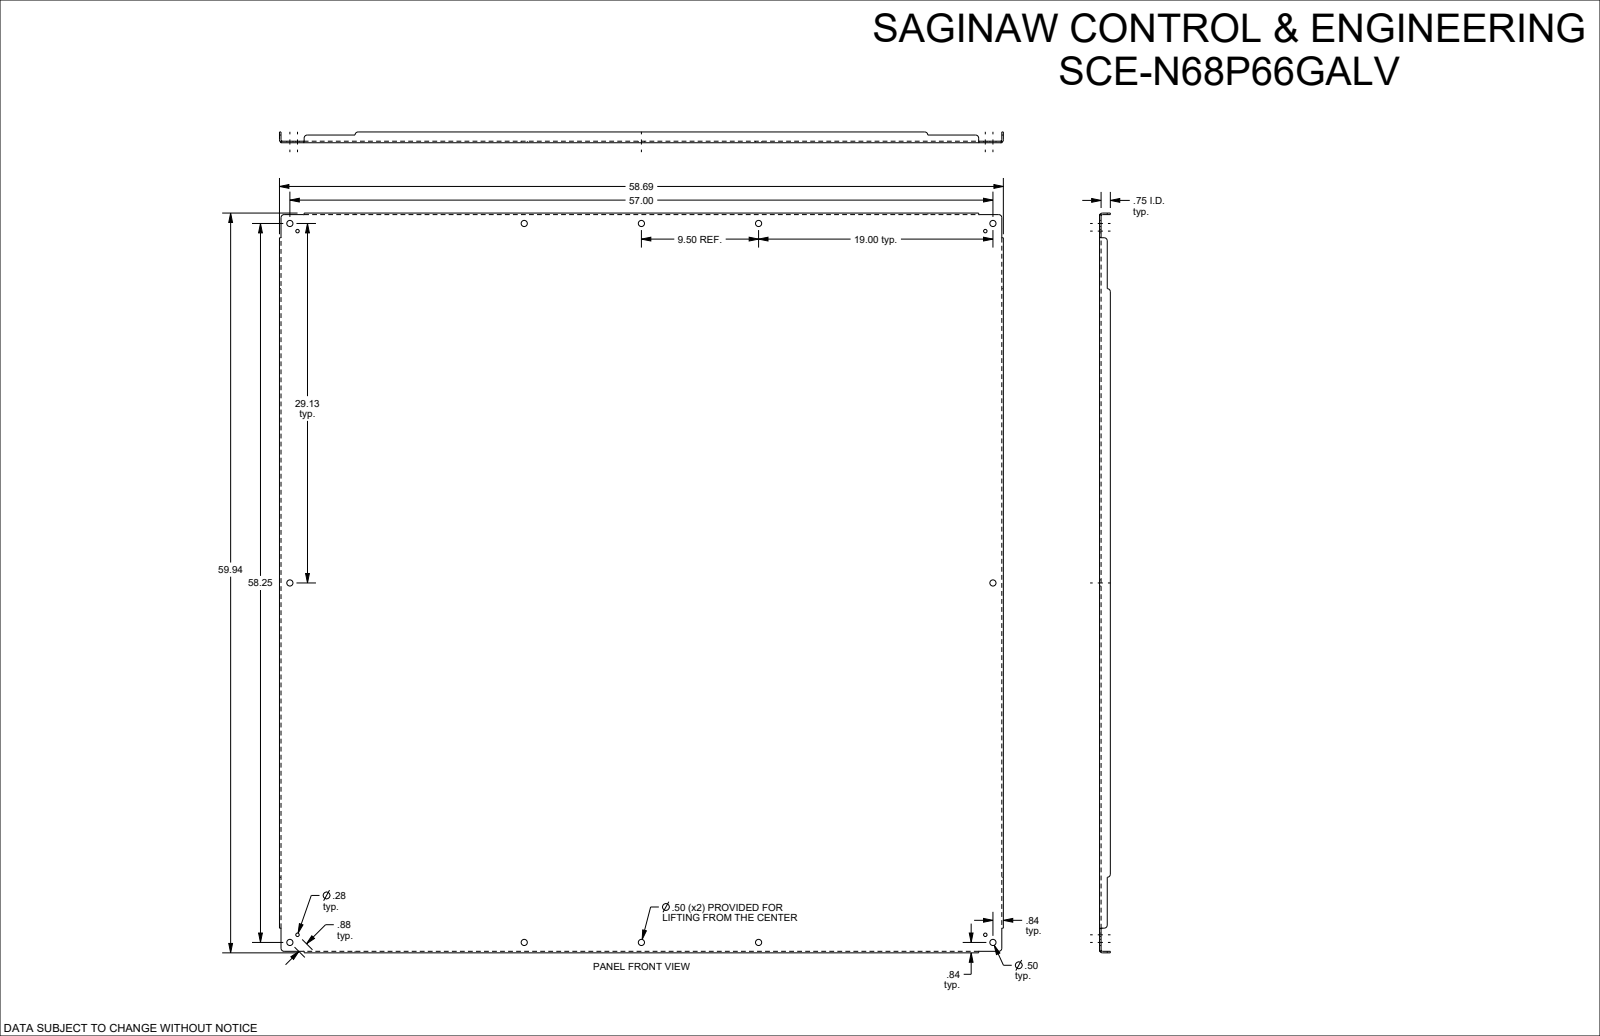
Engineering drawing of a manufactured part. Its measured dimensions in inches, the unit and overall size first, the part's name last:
Units: inches
Overall size (bounding box): 59.938 × 58.688 × 0.875
Round holes (diameter × count): ⌀0.5 ×12, ⌀0.281 ×4
Partial cylindrical surfaces — rounded edges, fillets, slot ends (radius × count): R0.25 ×12, R0.112 ×4, R0.237 ×4
Main face-to-face distances: 0.125, 58.563, 0.125, 59.813, 58.438, 58.687, 59.687, 59.938, 0.75, 0.875
Hole centre spacings: 19, 61.27, 58.25, 0.875, 9.5, 18.391, 27.888, 28.5
Volume: 456.7 in³ · Surface area: 7 341 in²
Bodies: 1 solid, 130 faces (46 planar, 60 cylindrical, 24 other)
Part name (STEP PRODUCT): SCE-N68P66GALV
STEP written by: SolidWorks 2023 (AUTOMOTIVE_DESIGN)
